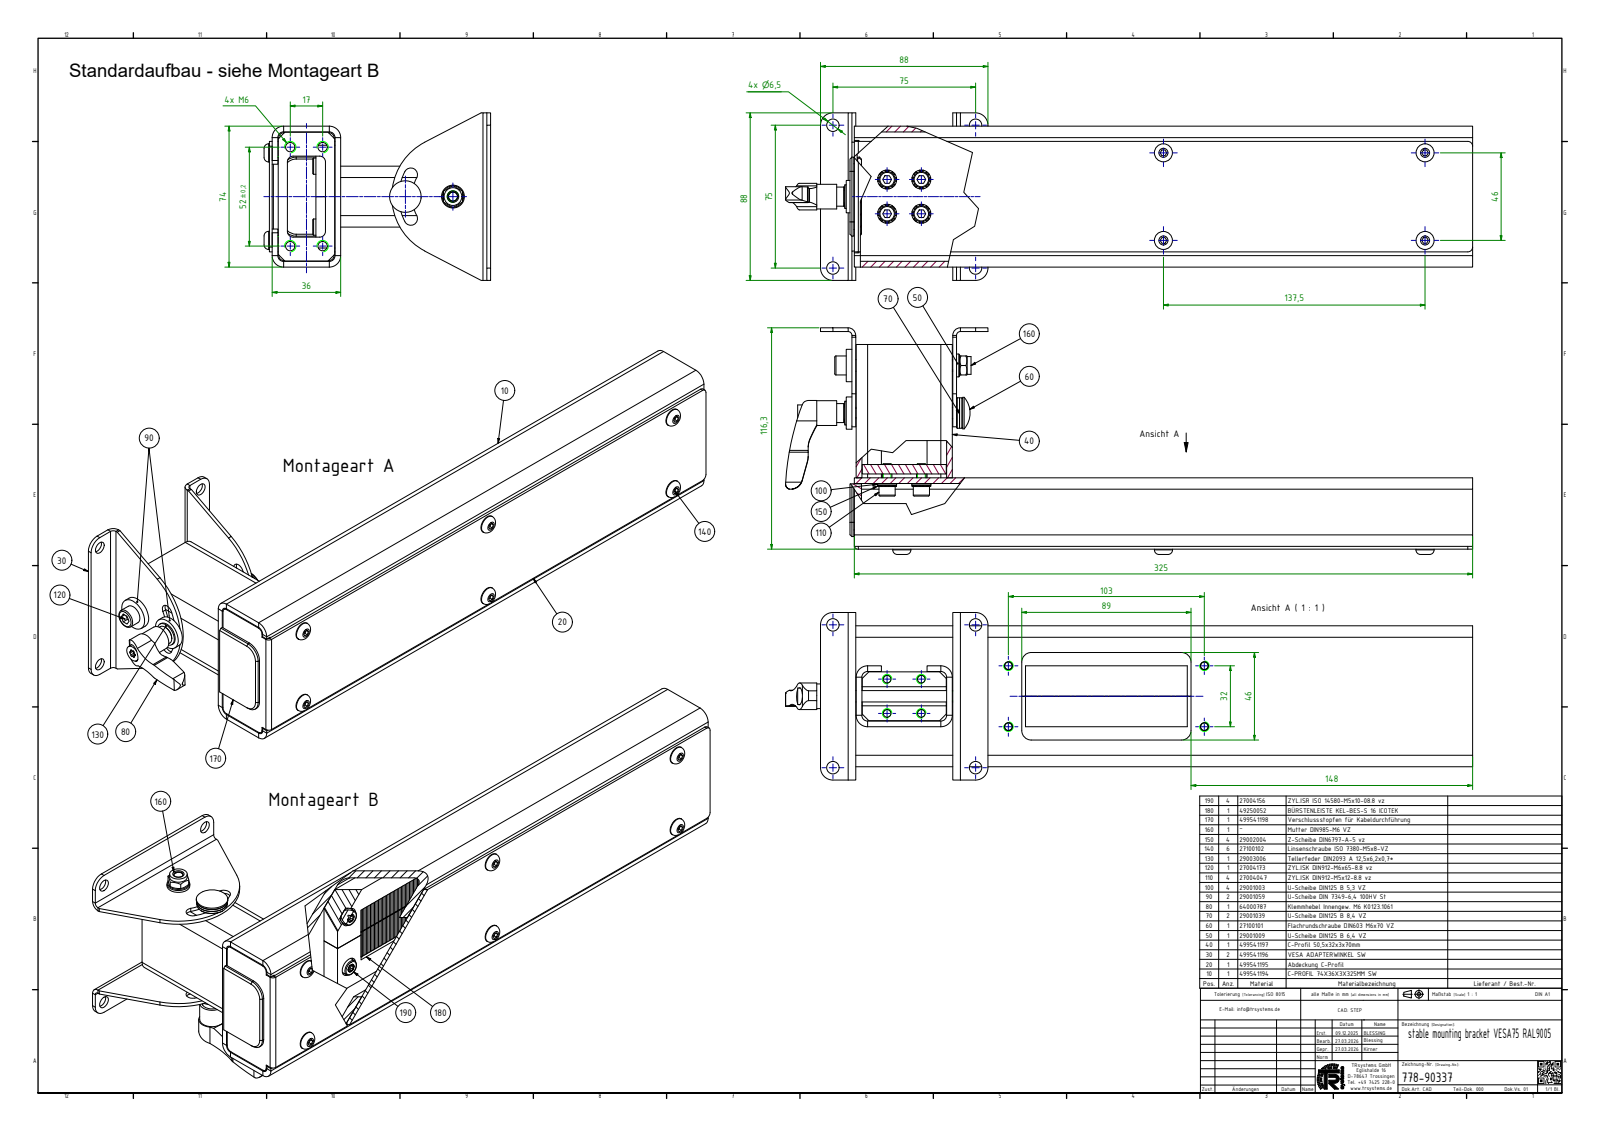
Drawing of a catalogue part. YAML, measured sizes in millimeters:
part_name: "778-90337_000; 49-954-1194_000; 49-954-1194_001; 49-954-1194-001_000 (+8 more)"
step_written_by: "Autodesk Inventor 2024 (AUTOMOTIVE_DESIGN)"
units: millimeters
bodies: {solids: 43, faces: 1081, planar: 420, cylindrical: 553, other: 108}
overall_size: [361.12, 119.06, 88]
volume: 306097
surface_area: 233233
round_holes:
  - {diameter: 4.13, count: 14}
  - {diameter: 5.5, count: 8}
  - {diameter: 4.92, count: 6}
  - {diameter: 6, count: 6}
  - {diameter: 6.5, count: 6}
  - {diameter: 5.3, count: 4}
  - {diameter: 10, count: 4}
  - {diameter: 6.4, count: 2}
  - {diameter: 6.2, count: 1}
  - {diameter: 7, count: 1}
  - {diameter: 8.4, count: 1}
  - {diameter: 8.6, count: 1}
round_bosses_or_shafts:
  - {diameter: 5, count: 15}
  - {diameter: 8.5, count: 8}
  - {diameter: 10, count: 6}
  - {diameter: 9.5, count: 6}
  - {diameter: 17, count: 2}
  - {diameter: 6, count: 2}
  - {diameter: 16.55, count: 1}
  - {diameter: 16, count: 1}
partial_cylinders:
  - {radius: 0.5, count: 85}
  - {radius: 0.15, count: 64}
  - {radius: 0.45, count: 30}
  - {radius: 0.79, count: 24}
  - {radius: 3, count: 12}
  - {radius: 2, count: 10}
  - {radius: 2.5, count: 8}
  - {radius: 6, count: 8}
face_to_face_distances: [3, 33, 1.5, 34.5, 36, 37.5, 71, 30, 50, 53]
hole_center_spacings: [54.54, 18, 40.31, 65.76, 75, 137.5, 144.99, 46]
